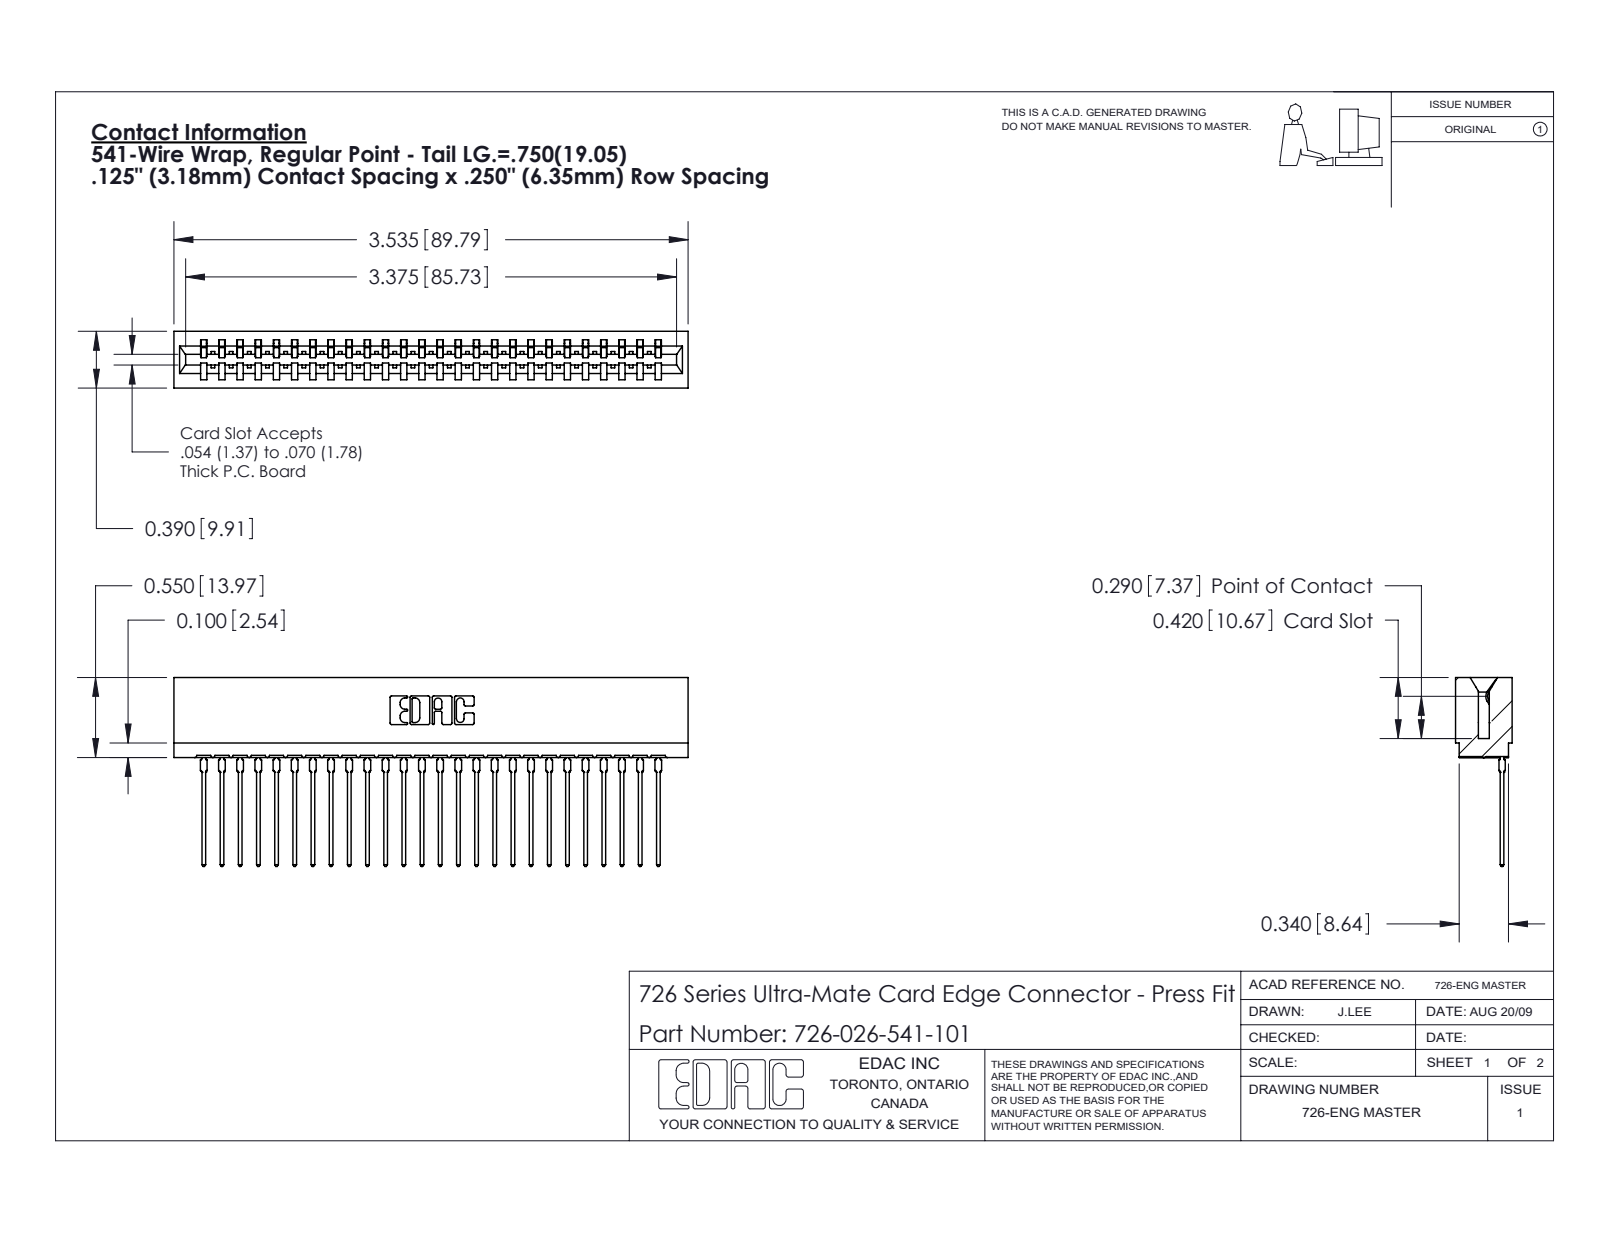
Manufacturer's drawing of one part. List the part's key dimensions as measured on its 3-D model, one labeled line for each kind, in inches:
Part name (STEP PRODUCT): 726 Part_.515 Slot Depth - 01; 726-026-541-101; 746-292-001_541
STEP written by: SolidWorks 2020 (CONFIG_CONTROL_DESIGN)
Units: inches
Bodies: 27 solids, 2905 faces (1693 planar, 536 cylindrical, 676 other)
Overall size (bounding box): 3.535 × 1.299 × 0.39
Volume: 0.502 in³ · Surface area: 20.07 in²
Partial cylindrical surfaces — rounded edges, fillets, slot ends (radius × count): R0.021 ×52, R0.015 ×27, R0.01 ×22, R0.007 ×6, R0.031 ×6, R0.005 ×4, R0.011 ×4, R0.026 ×3
Main face-to-face distances: 0.057, 0.333, 0.25, 0.39, 0.025, 0.307, 0.5, 0.083, 0.125, 0.75
